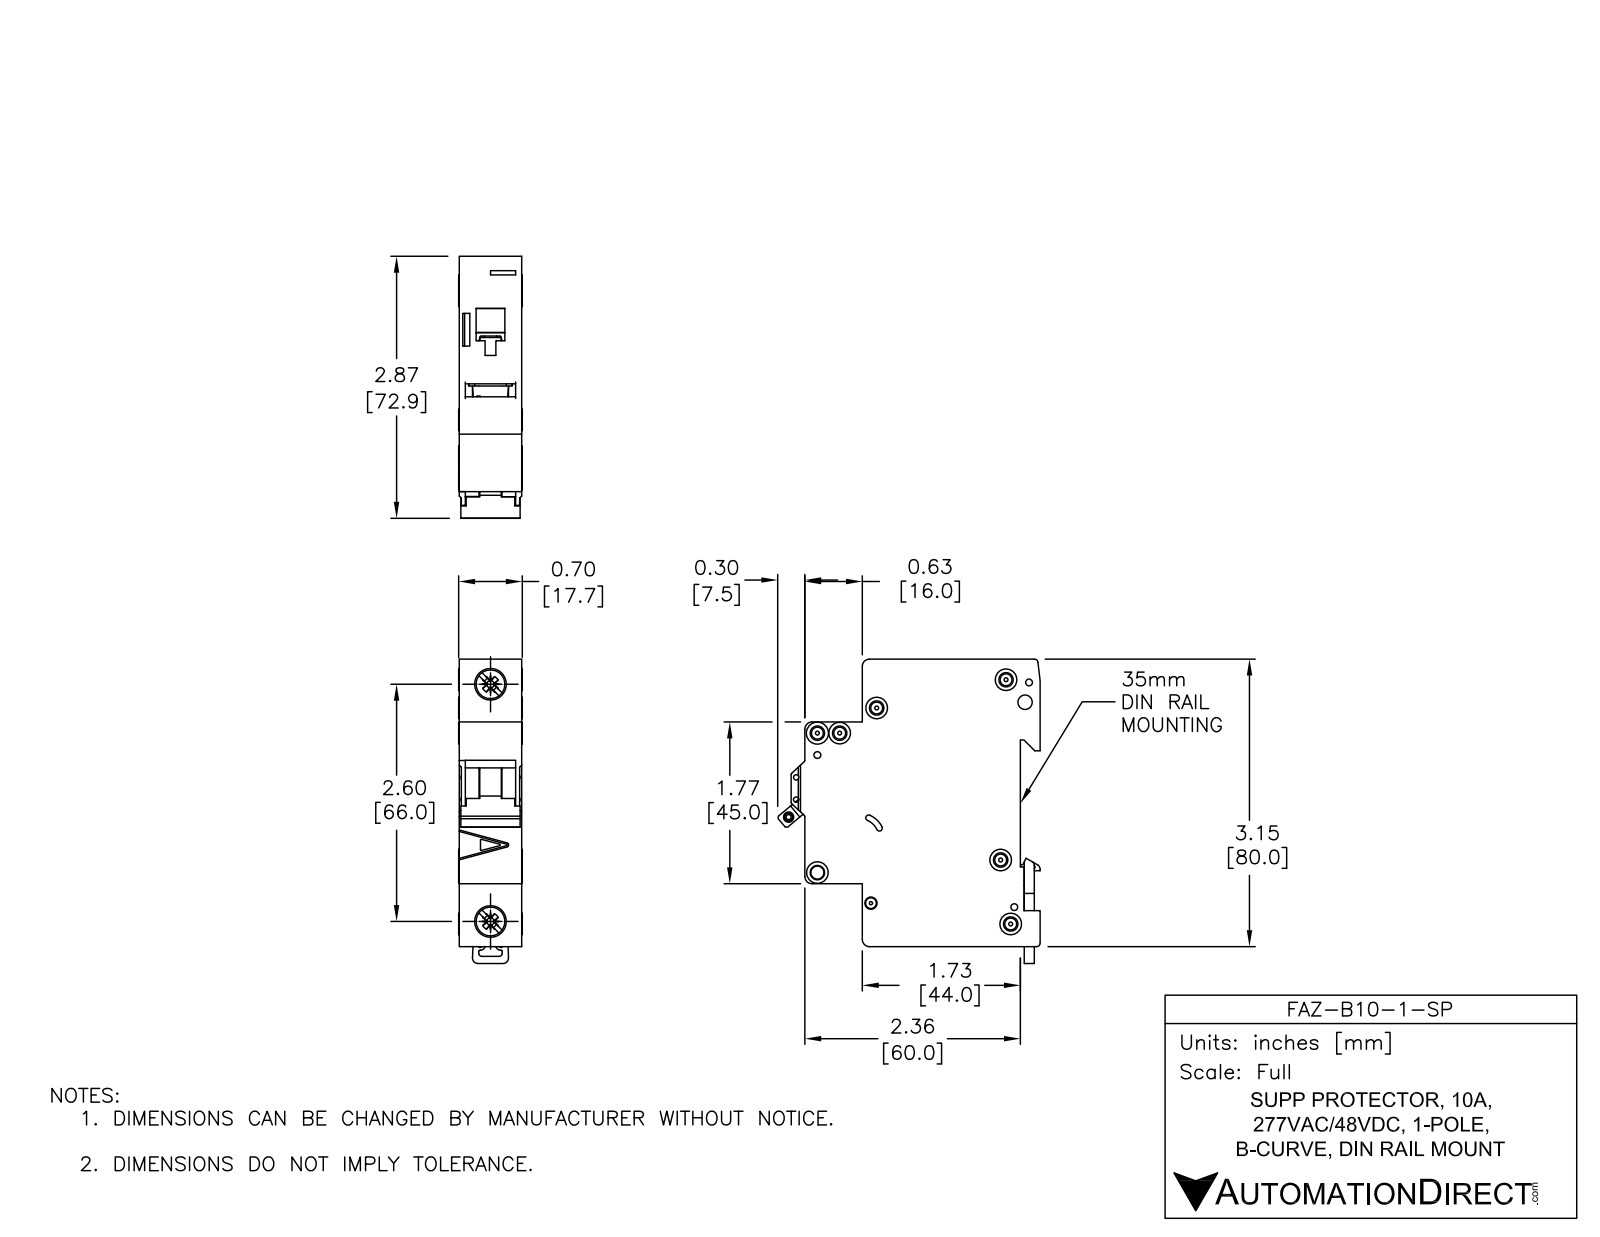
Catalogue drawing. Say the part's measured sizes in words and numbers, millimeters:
The part is named "FAZ-B10-1-SP". Its 3-D file was written by "SolidWorks 2014 (AUTOMOTIVE_DESIGN)". It is 5 solids with 558 faces: 235 planar, 202 cylindrical and 121 other. Overall it measures 84.78 by 73.04 by 17.7 millimeters. Its volume is 74 935 cubic millimeters and its surface area 19 545 square millimeters. Round holes: 6 of diameter 3.6, 3 of diameter 1.9, 2 of diameter 1.09, 2 of diameter 1.5, 2 of diameter 4, 2 of diameter 7.15, 1 of diameter 2.15, 1 of diameter 2.2, 1 of diameter 2.55, 1 of diameter 3.3, 1 of diameter 3.4. Round bosses or shafts: 4 of diameter 6, 2 of diameter 8.2, 1 of diameter 2.5. Partial cylindrical surfaces (rounded edges, fillets, slot ends): 30 of radius 0.25, 13 of radius 0.5, 8 of radius 2, 5 of radius 0.2, 4 of radius 1, 2 of radius 0.8, 2 of radius 3, 1 of radius 1.5. The main face-to-face distances are 17.5, 79.48, 5.5, 49.5, 44, 65.5, 60, 16, 1.75, 15.75. The hole center spacings are 6.2, 13.64, 4.81, 5.19, 5.61, 6.1, 6.44, 8.19.
